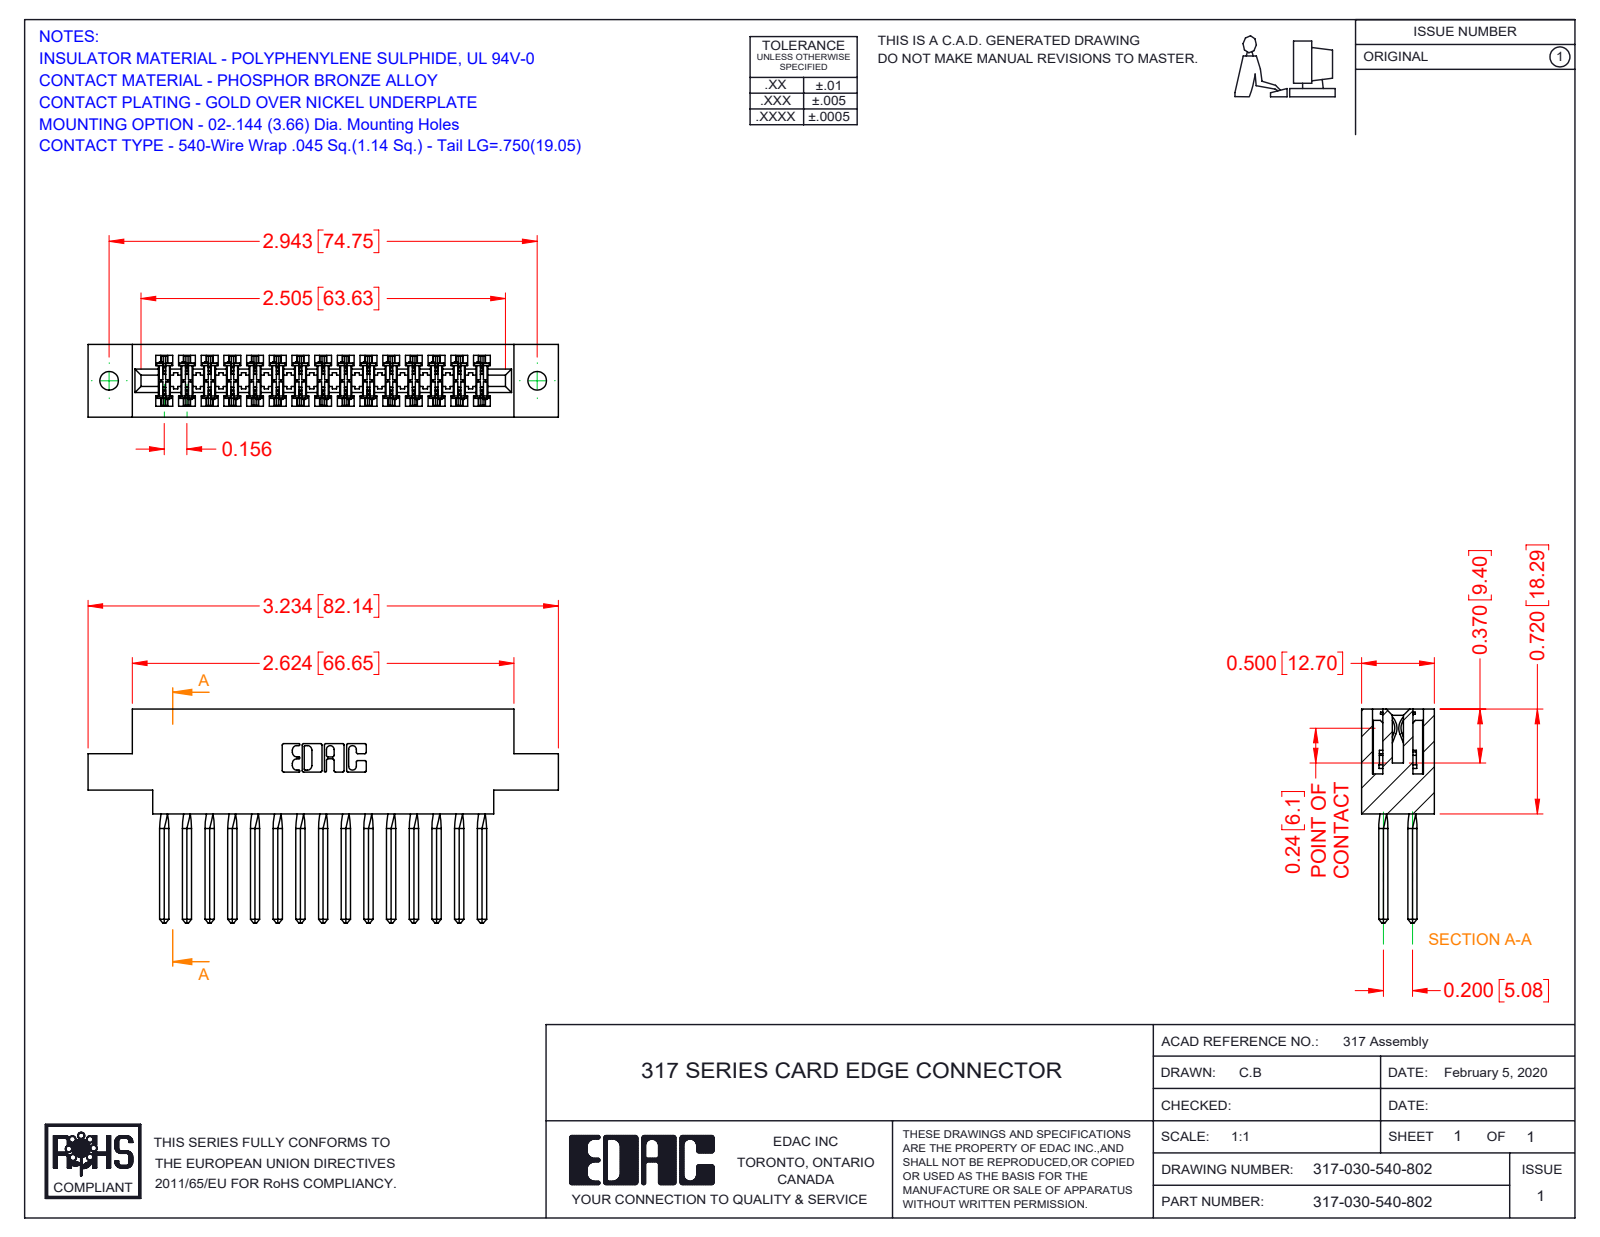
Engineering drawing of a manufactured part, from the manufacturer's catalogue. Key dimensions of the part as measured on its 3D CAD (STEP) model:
Part name (STEP PRODUCT): 317 Part_.144 Dia; 317-030-540-802; 317-290-001_540
STEP written by: SolidWorks 2016 (CONFIG_CONTROL_DESIGN)
Units: inches
Bodies: 31 solids, 2772 faces (2248 planar, 404 cylindrical, 120 other)
Overall size (bounding box): 3.234 × 1.47 × 0.5
Volume: 0.783 in³ · Surface area: 27.68 in²
Round holes (diameter × count): ⌀0.128 ×2
Partial cylindrical surfaces — rounded edges, fillets, slot ends (radius × count): R0.015 ×60, R0.01 ×22, R0.007 ×6, R0.031 ×6, R0.026 ×3, R0.095 ×2, R0.1 ×2, R0.11 ×2
Main face-to-face distances: 0.5, 0.075, 0.425, 0.11, 0.35, 0.22, 0.72, 0.195, 0.116, 0.211
Hole centre spacings: 2.943
